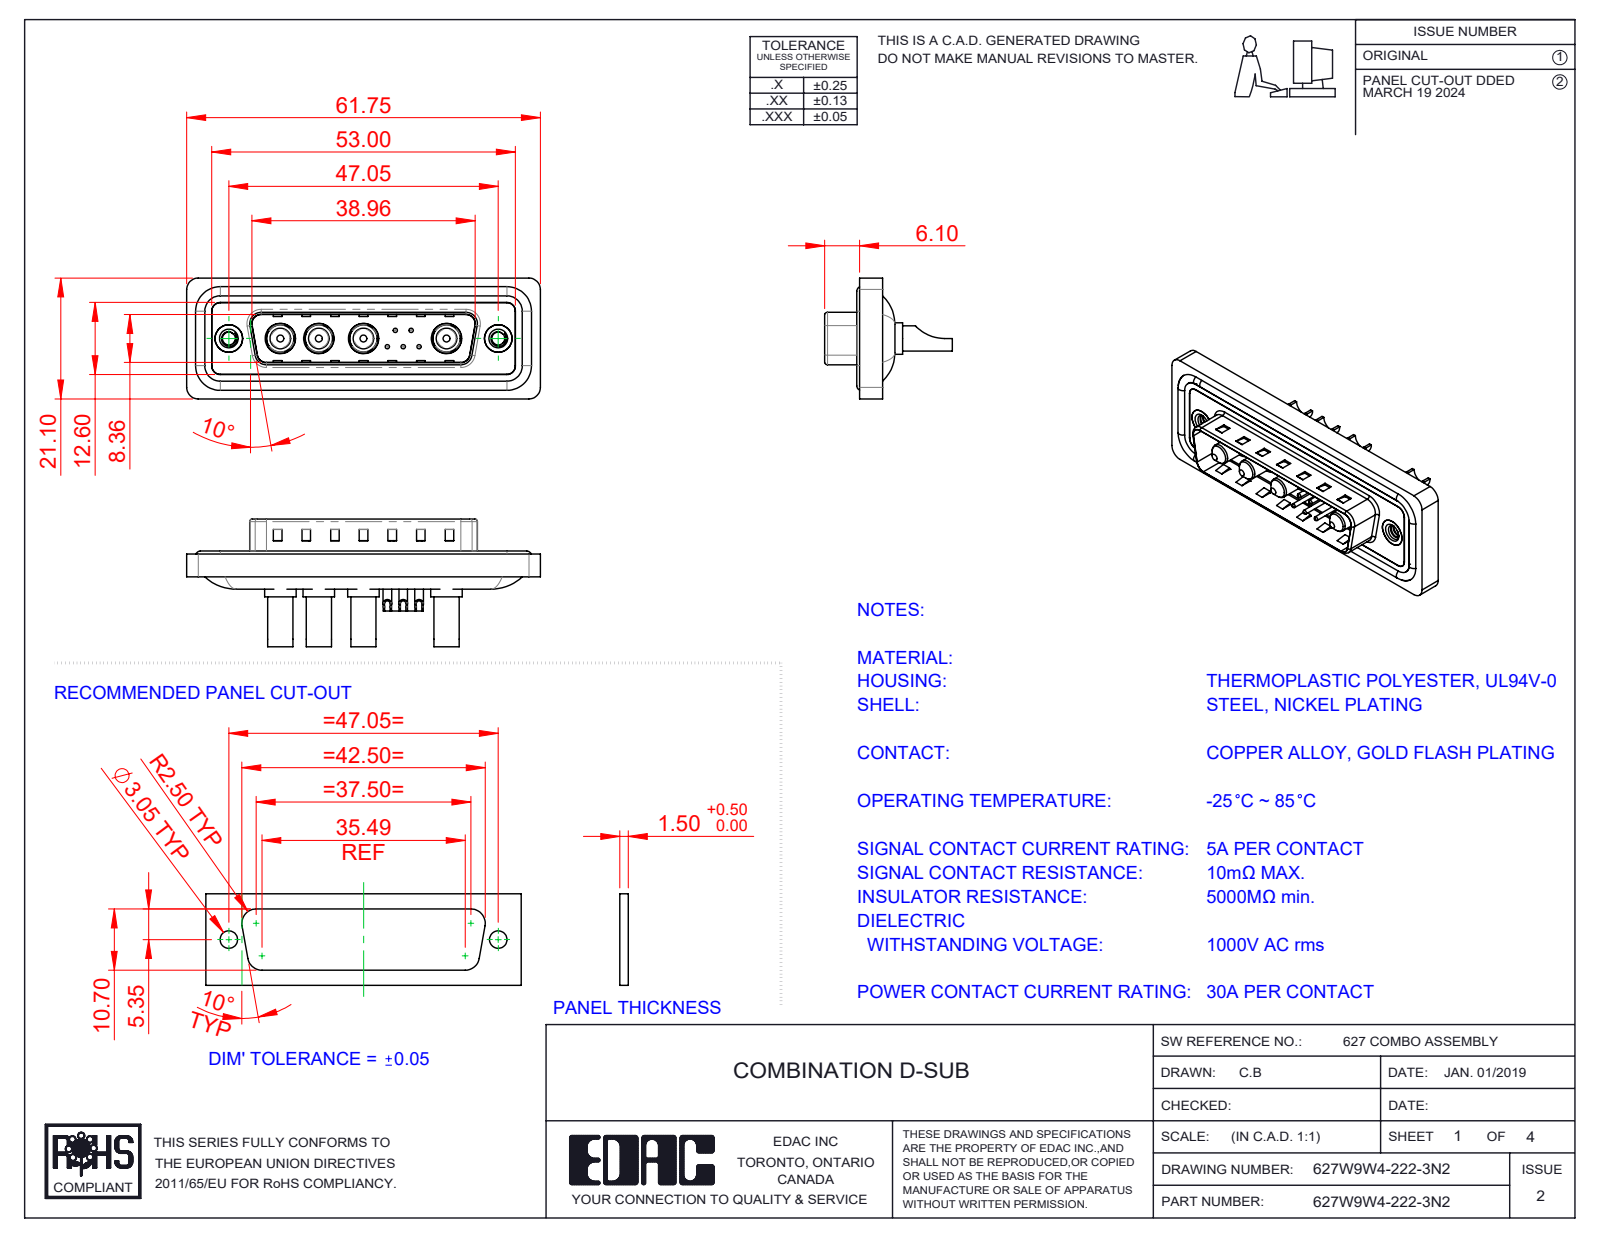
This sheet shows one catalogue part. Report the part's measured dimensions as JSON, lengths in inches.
{"part_name": "627Combo Contact Row 2_22; 627Combo Shell Rear_25 Contacts; 627Combo Waterproof Housing_25 Contacts; 627Combo Threaded Rivet_2 (+5 more)", "step_written_by": "SolidWorks 2023 (CONFIG_CONTROL_DESIGN)", "units": "inches", "bodies": {"solids": 20, "faces": 848, "planar": 306, "cylindrical": 356, "other": 186}, "overall_size": [2.431, 0.878, 0.831], "volume_in3": 0.458, "surface_area_in2": 19.07, "round_holes": [[0.03, 5], [0.039, 5], [0.063, 5], [0.079, 5], [0.138, 4], [0.191, 4], [0.209, 4], [0.089, 2], [0.157, 2], [0.189, 2], [0.197, 2]], "round_bosses_or_shafts": [[0.059, 5], [0.217, 4], [0.205, 4], [0.187, 4], [0.173, 4], [0.148, 4], [0.142, 4], [0.063, 4]], "partial_cylinders_radius": [[0.059, 22], [0.079, 18], [0.02, 8], [0.063, 8], [0.039, 6], [0.01, 4], [0.024, 4], [0.026, 4]], "face_to_face_distances": [0.016, 0.059, 0.043, 0.02, 0.063, 0.122, 0.114, 0.032, 0.377, 0.222], "hole_center_spacings": [0.124, 0.109, 0.198, 0.571, 0.109, 0.173, 0.174, 0.197]}
